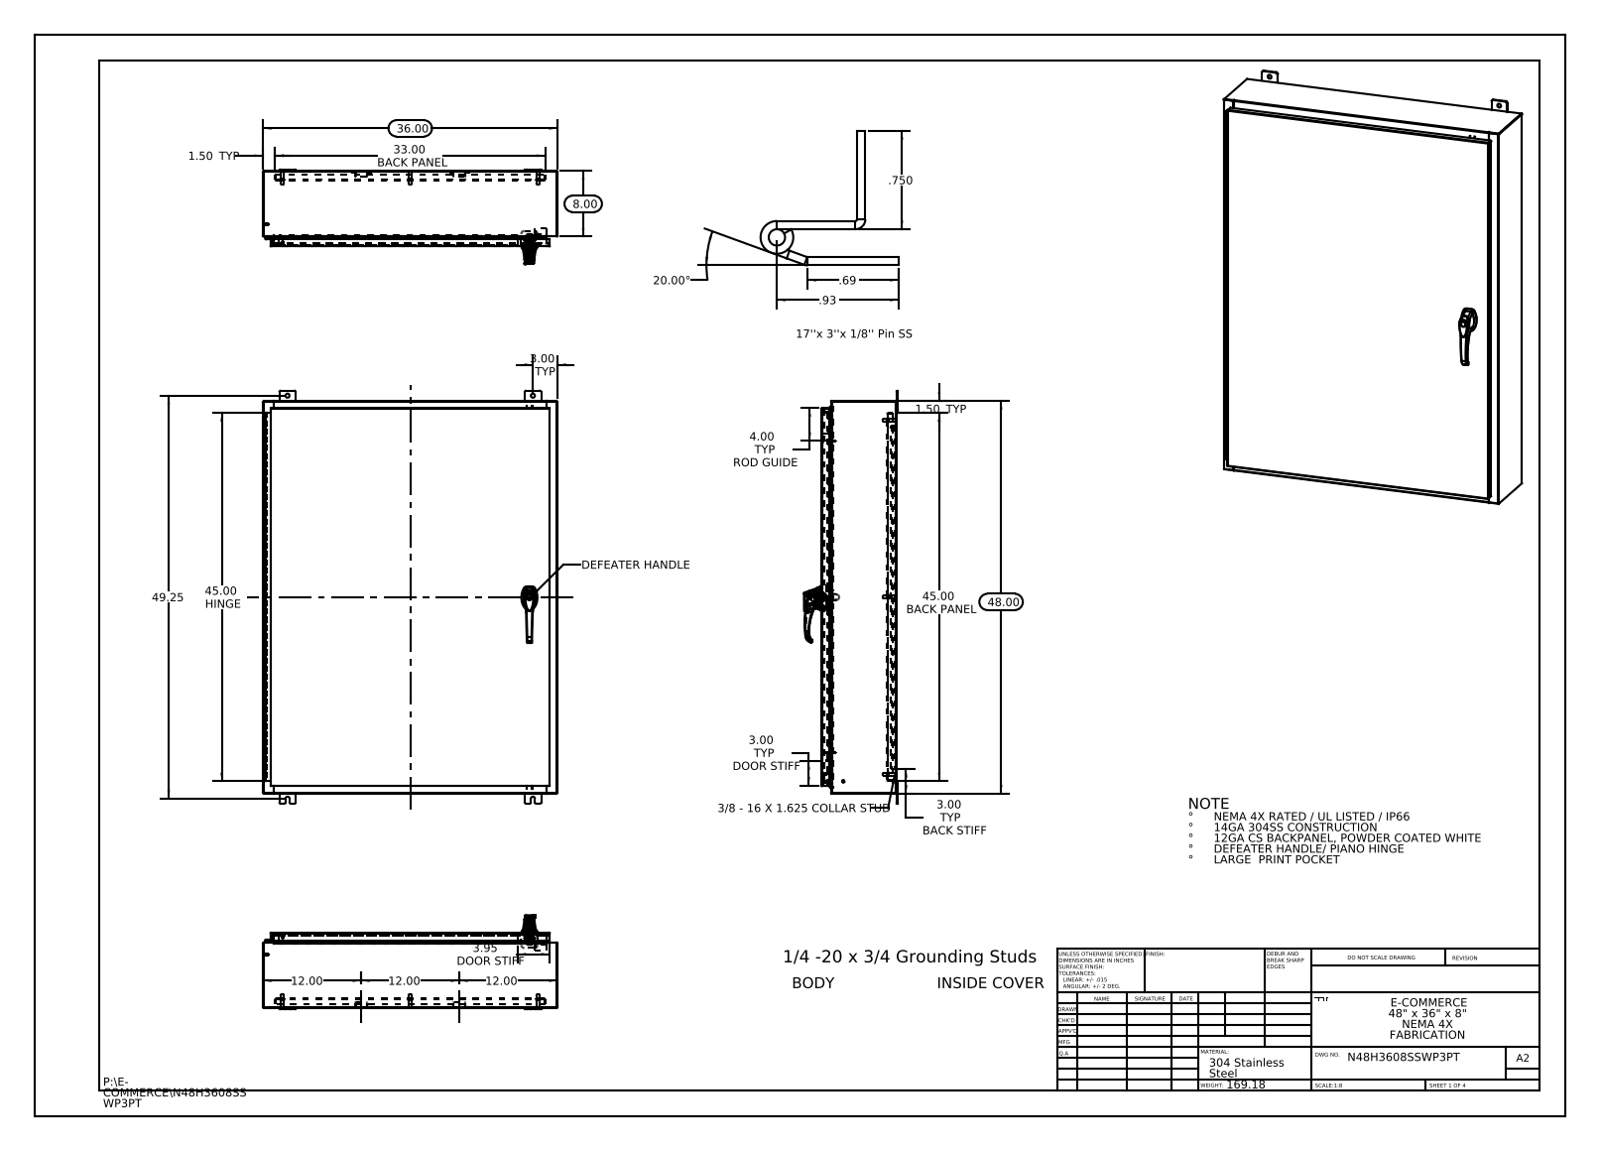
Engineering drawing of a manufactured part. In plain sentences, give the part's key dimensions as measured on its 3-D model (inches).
The part is named "297025; 297026; N48H3608SSWP3PT Hinge Cover Side; 012103_012102 (+8 more)". Its 3-D file was written by "SolidWorks 2013 (CONFIG_CONTROL_DESIGN)". It is 51 solids with 3400 faces: 1309 planar, 1305 cylindrical and 786 other. Overall it measures 50.5 by 36 by 11.495 inches. Its volume is 606.1 cubic inches and its surface area 14 968 square inches. Round holes: 12 of diameter 0.5, 10 of diameter 0.25, 3 of diameter 0.138, 3 of diameter 0.161, 2 of diameter 0.079, 2 of diameter 0.203, 2 of diameter 0.313, 2 of diameter 0.437, 1 of diameter 0.125, 1 of diameter 0.125, 1 of diameter 0.197, 1 of diameter 0.276. Round bosses or shafts: 10 of diameter 0.157, 10 of diameter 0.14, 8 of diameter 0.625, 8 of diameter 0.375, 8 of diameter 0.33, 3 of diameter 0.315, 3 of diameter 0.236, 1 of diameter 1.181. Partial cylindrical surfaces (rounded edges, fillets, slot ends): 37 of radius 0.118, 34 of radius 0.013, 33 of radius 0.006, 28 of radius 0.088, 24 of radius 0.19, 15 of radius 0.039, 12 of radius 0.028, 6 of radius 0.008. The main face-to-face distances are 0.075, 9.126, 9.051, 9.201, 0.104, 1, 8.126, 1.075, 8.051, 1.179. The hole center spacings are 17.357, 19.665, 21.625, 38.003, 45.986, 31.25, 43.25, 0.295.
